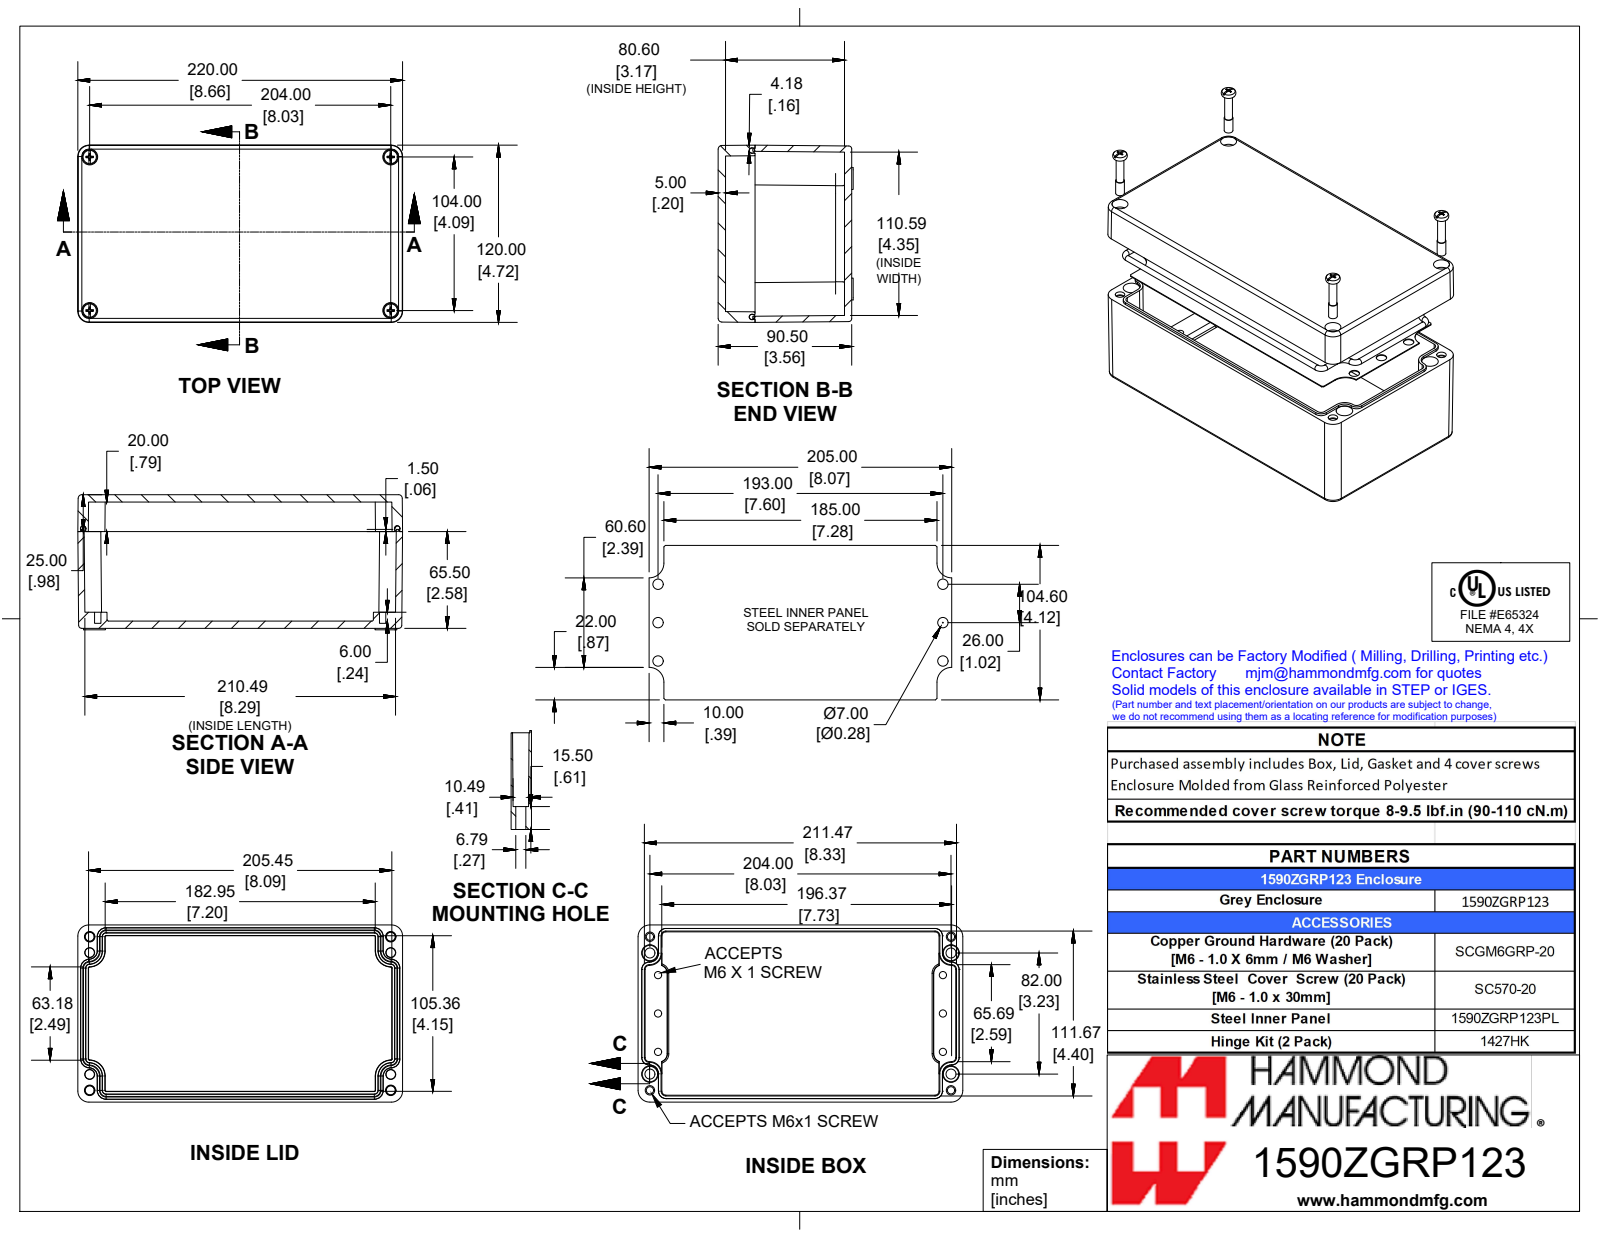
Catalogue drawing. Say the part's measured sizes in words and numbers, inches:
The part is named "1590ZGRP123". Its 3-D file was written by "SolidWorks 2019 (CONFIG_CONTROL_DESIGN)". It is 8 solids with 479 faces: 233 planar, 94 cylindrical and 152 other. Overall it measures 8.661 by 4.724 by 3.602 inches. Its volume is 35.89 cubic inches and its surface area 439.6 square inches. Round holes: 10 of diameter 0.194, 6 of diameter 0.276, 4 of diameter 0.236, 4 of diameter 0.252, 4 of diameter 0.268, 4 of diameter 0.425. Round bosses or shafts: 6 of diameter 0.148, 4 of diameter 0.231, 4 of diameter 0.208. Partial cylindrical surfaces (rounded edges, fillets, slot ends): 20 of radius 0.059, 4 of radius 0.079, 4 of radius 0.098, 4 of radius 0.295, 4 of radius 0.315, 4 of radius 0.394, 2 of radius 0.039. The main face-to-face distances are 3.563, 0.165, 0.429, 3.134, 3.366, 2.937, 0.197, 3.114, 0.02, 0.449. The hole center spacings are 0.433, 0.629, 1.024, 1.046, 1.629, 2.059, 2.647, 3.078.
